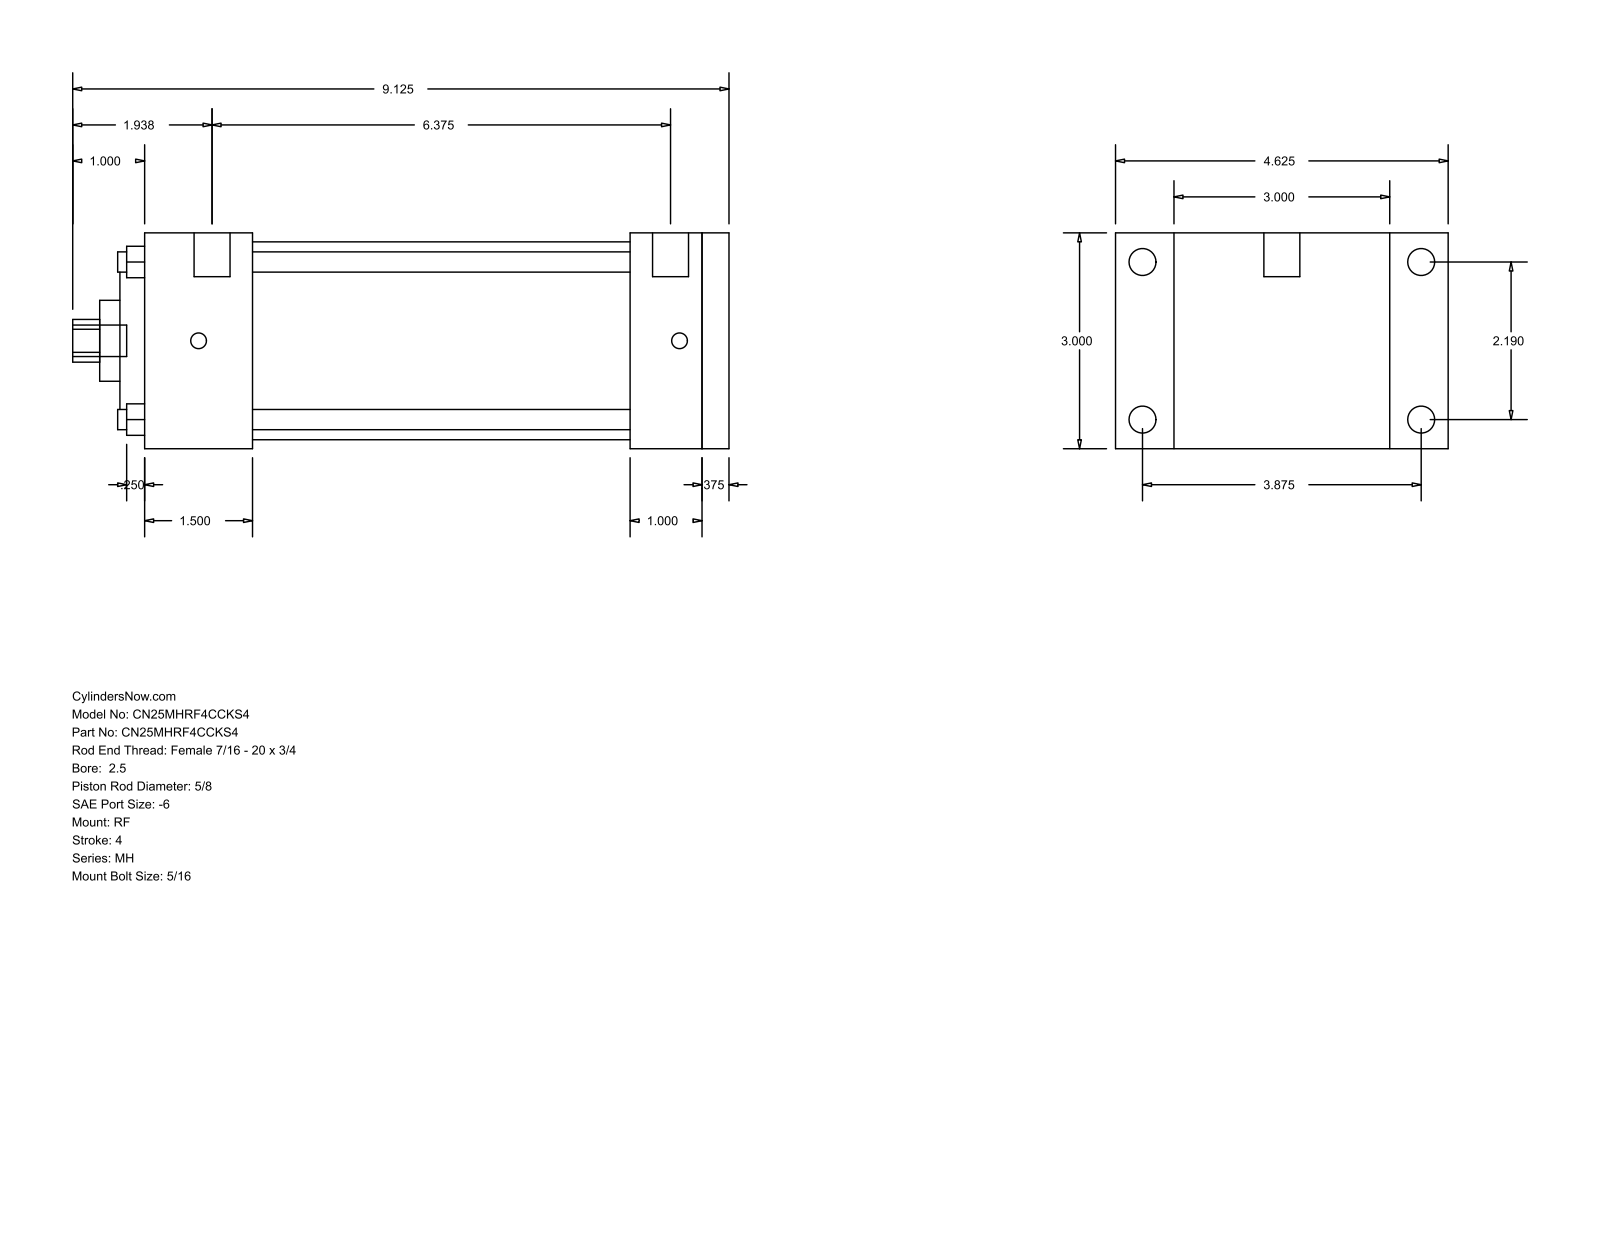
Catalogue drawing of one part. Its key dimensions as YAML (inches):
part_name: "MH_RF__0250_0.625"
step_written_by: "GSSL Pune (CONFIG_CONTROL_DESIGN)"
units: inches
bodies: {solids: 0, faces: 94, planar: 65, cylindrical: 29, other: 0}
overall_size: [9.125, 4.625, 3]
round_holes:
  - {diameter: 0.281, count: 4}
  - {diameter: 0.625, count: 1}
  - {diameter: 1.125, count: 1}
  - {diameter: 2.187, count: 1}
  - {diameter: 2.75, count: 1}
round_bosses_or_shafts:
  - {diameter: 0.375, count: 4}
  - {diameter: 0.219, count: 4}
  - {diameter: 0.5, count: 2}
  - {diameter: 0.437, count: 1}
partial_cylinders:
  - {radius: 0.297, count: 1}
face_to_face_distances: [3, 0.375, 8.125, 7.75, 1, 6.75, 1.375, 1.5, 5.25, 6.25]
hole_center_spacings: [1.548, 2.19, 3.097]
